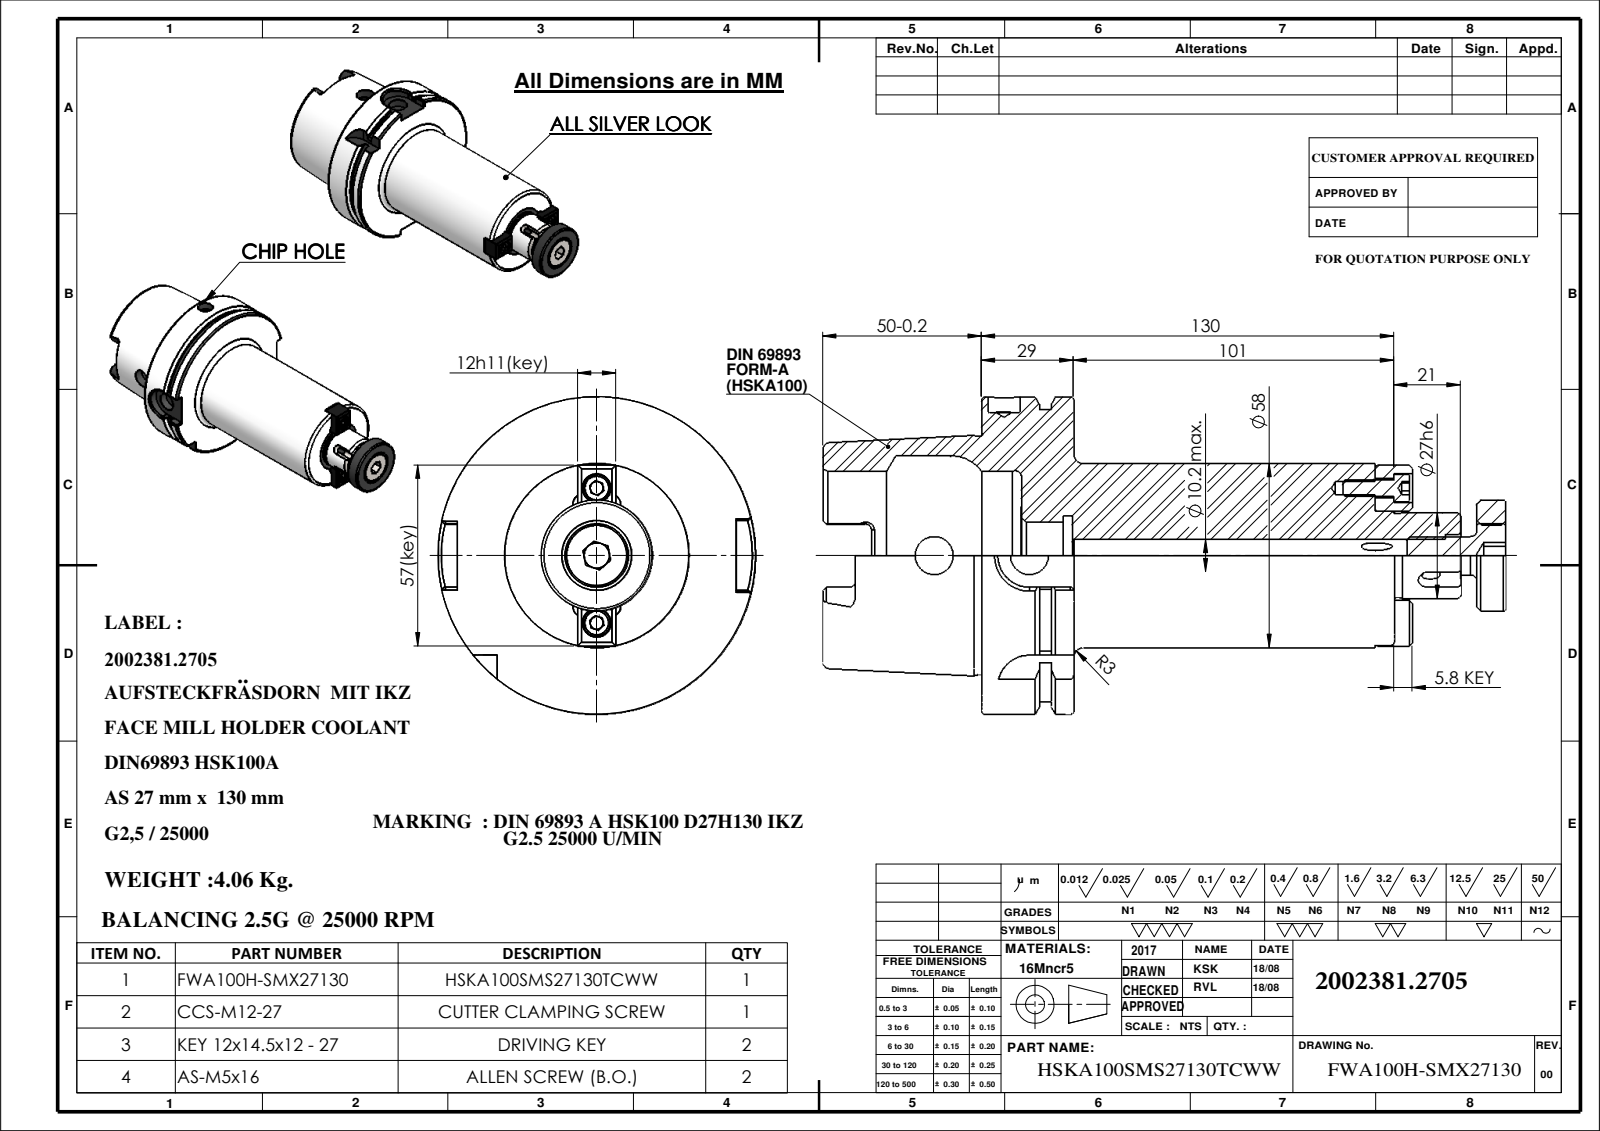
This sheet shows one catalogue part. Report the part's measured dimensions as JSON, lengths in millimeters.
{"part_name": "CCS-M12-27-1; CCS-M12-27-2; 91100A-AS527130; HSKA100SMS27130TCWW (+3 more)", "step_written_by": "SolidWorks 2009 (CONFIG_CONTROL_DESIGN)", "units": "millimeters", "bodies": {"solids": 7, "faces": 387, "planar": 149, "cylindrical": 104, "other": 134}, "overall_size": [215, 100, 100], "volume_mm3": 533438, "surface_area_mm2": 83096, "round_holes": [[3, 4], [4.2, 2], [6, 2], [9, 2], [12, 2], [8.4, 1], [10, 1], [10.2, 1], [13, 1], [19, 1], [21, 1], [25, 1]], "round_bosses_or_shafts": [[8.5, 2], [5, 2], [100, 1], [92, 1], [75.16, 1], [58, 1], [35, 1], [27, 1]], "partial_cylinders_radius": [[1.8, 6], [2, 4], [3, 4], [4.88, 4], [10, 2], [11, 1]], "face_to_face_distances": [28.95, 12.5, 16.45, 117.5, 130, 101.05, 50, 62.5, 78.95, 180], "hole_center_spacings": [21.25, 30, 42.5]}
